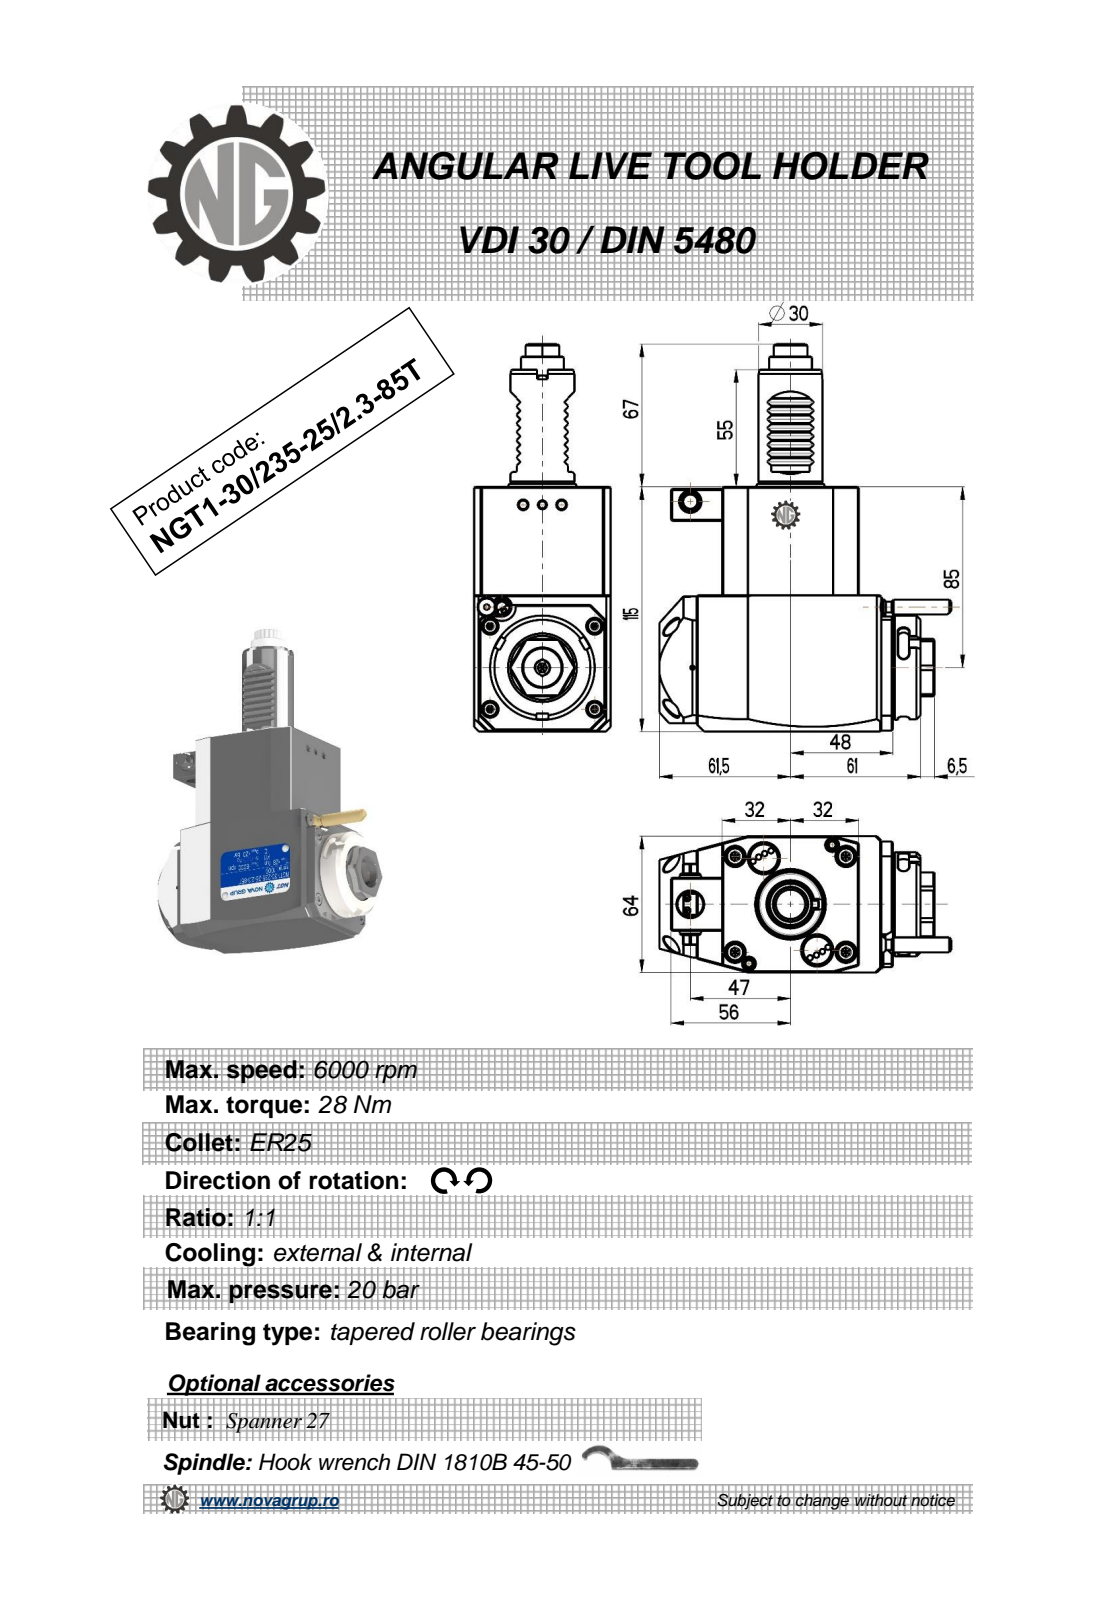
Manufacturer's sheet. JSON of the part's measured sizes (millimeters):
{"part_name": "NGT1_30_235_25_1_3_85T", "step_written_by": "PRO/ENGINEER BY PARAMETRIC TECHNOLOGY CORPORATION, 2010280 (CONFIG_CONTROL_DESIGN)", "units": "millimeters", "bodies": {"solids": 1, "faces": 466, "planar": 215, "cylindrical": 161, "other": 90}, "overall_size": [182, 136.88, 64], "volume_mm3": 677706, "surface_area_mm2": 58598, "round_holes": [[2.5, 1], [3, 1], [9.5, 1], [12, 1], [18, 1]], "round_bosses_or_shafts": [[8, 2], [49, 1], [42, 1], [30, 1], [20, 1], [10, 1], [7, 1], [5, 1]], "partial_cylinders_radius": [[1.98, 36], [0.3, 16], [2.5, 6], [180, 2], [3.85, 1], [4.25, 1], [4.5, 1], [7.08, 1]], "face_to_face_distances": [64, 115, 16, 80, 13, 51, 29.5, 122.5, 93.5, 109.5], "hole_center_spacings": [34.25, 51.62, 76.5]}
